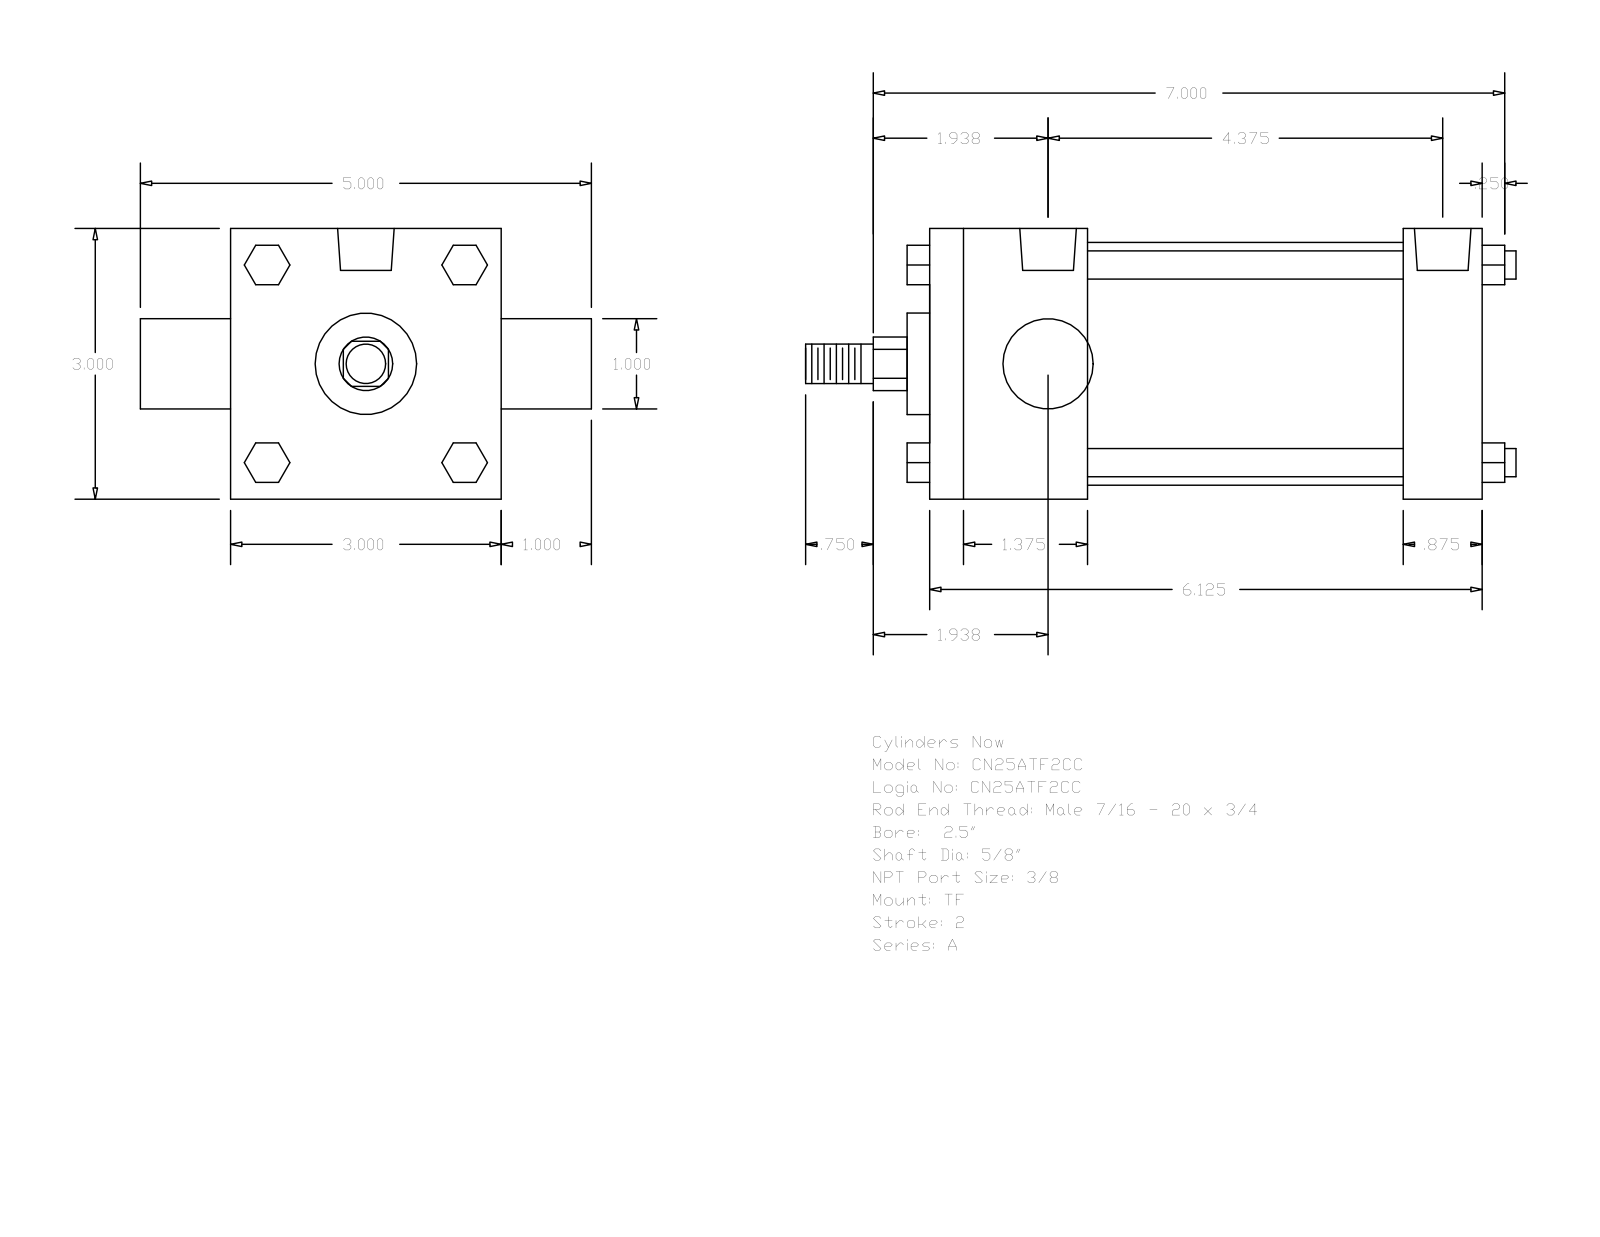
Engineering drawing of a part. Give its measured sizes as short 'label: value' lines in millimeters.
name: A_TF__0250_0.625
written by: GSSL Pune (CONFIG_CONTROL_DESIGN)
unit: mm
bodies: 0 solids, 120 faces (92 planar, 28 cylindrical, 0 other)
size: 200.03 × 127 × 76.2
holes: 3× ⌀5.56, 2× ⌀15.93
bosses: 4× ⌀7.94, 1× ⌀68.33, 1× ⌀28.57, 1× ⌀25.4, 1× ⌀15.88, 1× ⌀11.11
rounds: 1× R7.54
face distances: 76.2, 155.57, 44.45, 133.34, 88.89, 111.12, 22.23, 25.4, 101.6, 6.35
hole spacings: 2.38, 113.51, 111.13, 115.89
